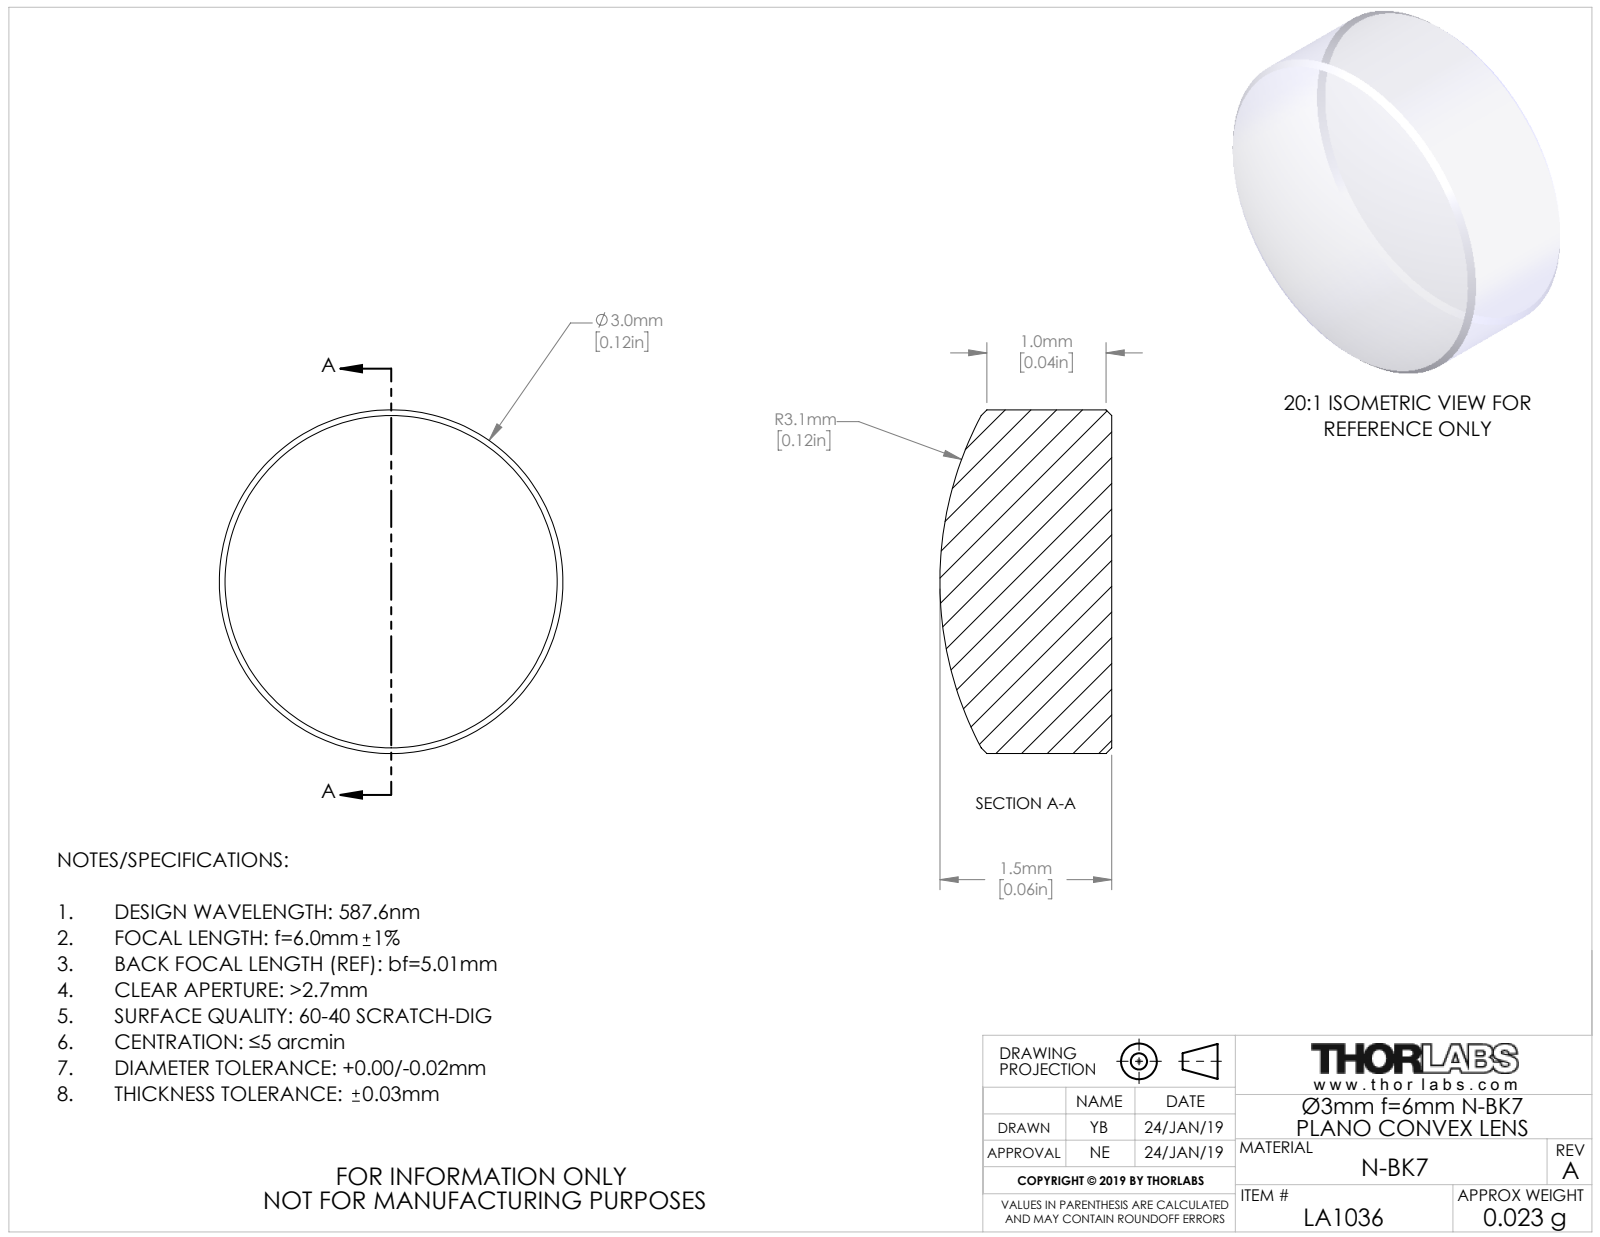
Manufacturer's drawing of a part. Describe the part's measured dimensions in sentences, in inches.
The part is named "TTN162580-E0W". Its 3-D file was written by "SolidWorks 2018 (CONFIG_CONTROL_DESIGN)". It is 1 solid with 9 faces: 1 planar, 2 cylindrical and 6 other. Overall it measures 0.118 by 0.118 by 0.059 inches. Its volume is 0.001 cubic inches and its surface area 0.039 square inches. Round bosses or shafts: 1 of diameter 0.118.
